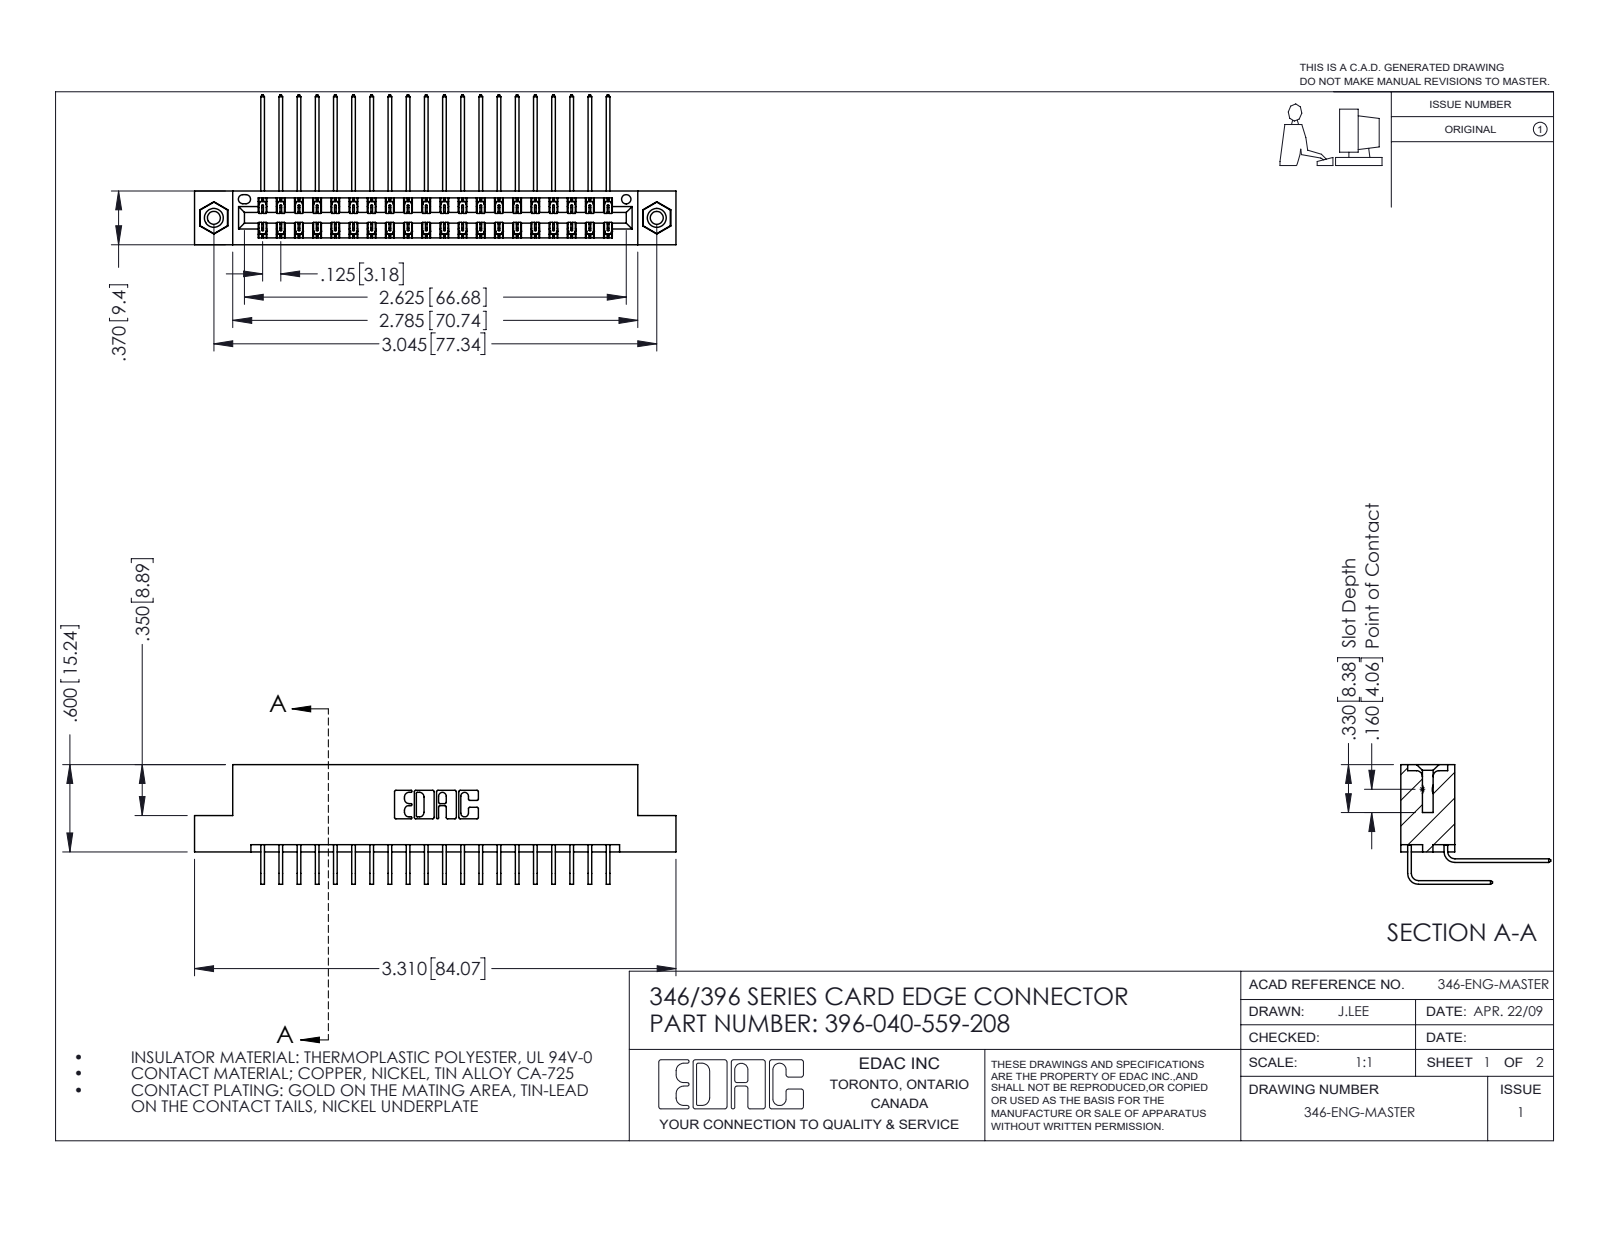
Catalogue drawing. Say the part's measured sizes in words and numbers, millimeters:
The part is named "346 Part_Flush Mounting Lugs - 0.156 Dia-TI; 396-040-559-208; 345-292-001_559 Tail - 2; 345-250-001_345-250-003-102 (+1 more)". Its 3-D file was written by "SolidWorks 2016 (CONFIG_CONTROL_DESIGN)". It is 43 solids with 2342 faces: 1588 planar, 738 cylindrical and 16 other. Overall it measures 84.1 by 26.2 by 20.9 millimeters. Its volume is 8 260 cubic millimeters and its surface area 12 120 square millimeters. Round holes: 2 of diameter 2.3, 2 of diameter 3.2, 2 of diameter 4, 1 of diameter 1.6. Round bosses or shafts: 2 of diameter 3.9. Partial cylindrical surfaces (rounded edges, fillets, slot ends): 60 of radius 0.2, 22 of radius 0.3, 6 of radius 0.2, 6 of radius 0.8, 3 of radius 0.7, 2 of radius 0.4, 2 of radius 0.6, 2 of radius 0.6. The main face-to-face distances are 1.2, 8.2, 6.4, 0.6, 9.4, 1.8, 7.6, 7, 3.8, 5.6. The hole center spacings are 6.2, 72.1, 77.3.
